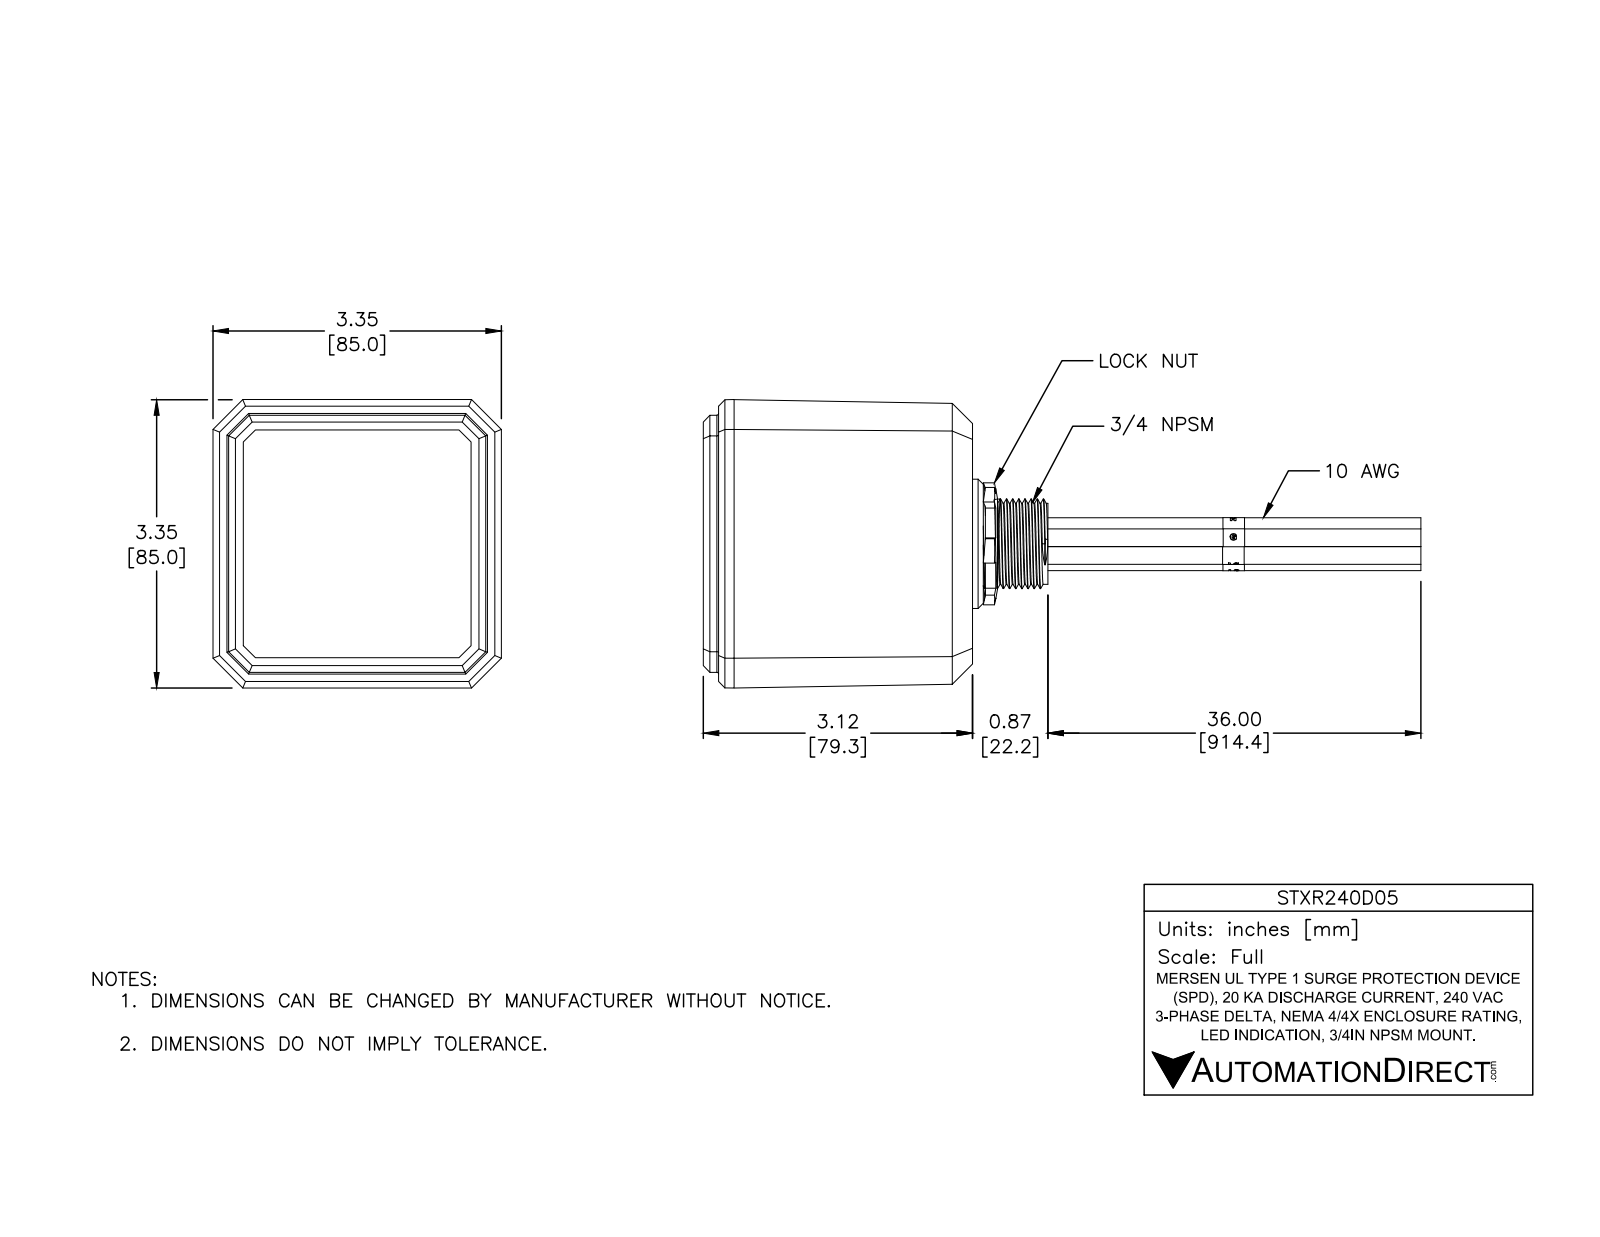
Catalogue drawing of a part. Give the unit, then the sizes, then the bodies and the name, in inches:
Units: inches
Overall size (bounding box): 8.327 × 3.347 × 3.347
Round holes (diameter × count): ⌀1 ×1
Round bosses / shafts (diameter × count): ⌀0.205 ×12, ⌀0.205 ×3, ⌀0.145 ×3, ⌀1.5 ×1, ⌀0.94 ×1, ⌀0.145 ×1
Partial cylindrical surfaces — rounded edges, fillets, slot ends (radius × count): R0.015 ×16, R0.02 ×8, R0.1 ×8, R0.04 ×4, R0.31 ×1, R0.639 ×1
Main face-to-face distances: 0.125, 0.125, 0.12, 2.989, 3.109, 2.864, 2.984, 2.766, 2.641, 0.223
Volume: 8.231 in³ · Surface area: 144.4 in²
Bodies: 7 solids, 510 faces (315 planar, 115 cylindrical, 80 other)
Part name (STEP PRODUCT): STXR240D05
STEP written by: SolidWorks 2016 (AUTOMOTIVE_DESIGN)
